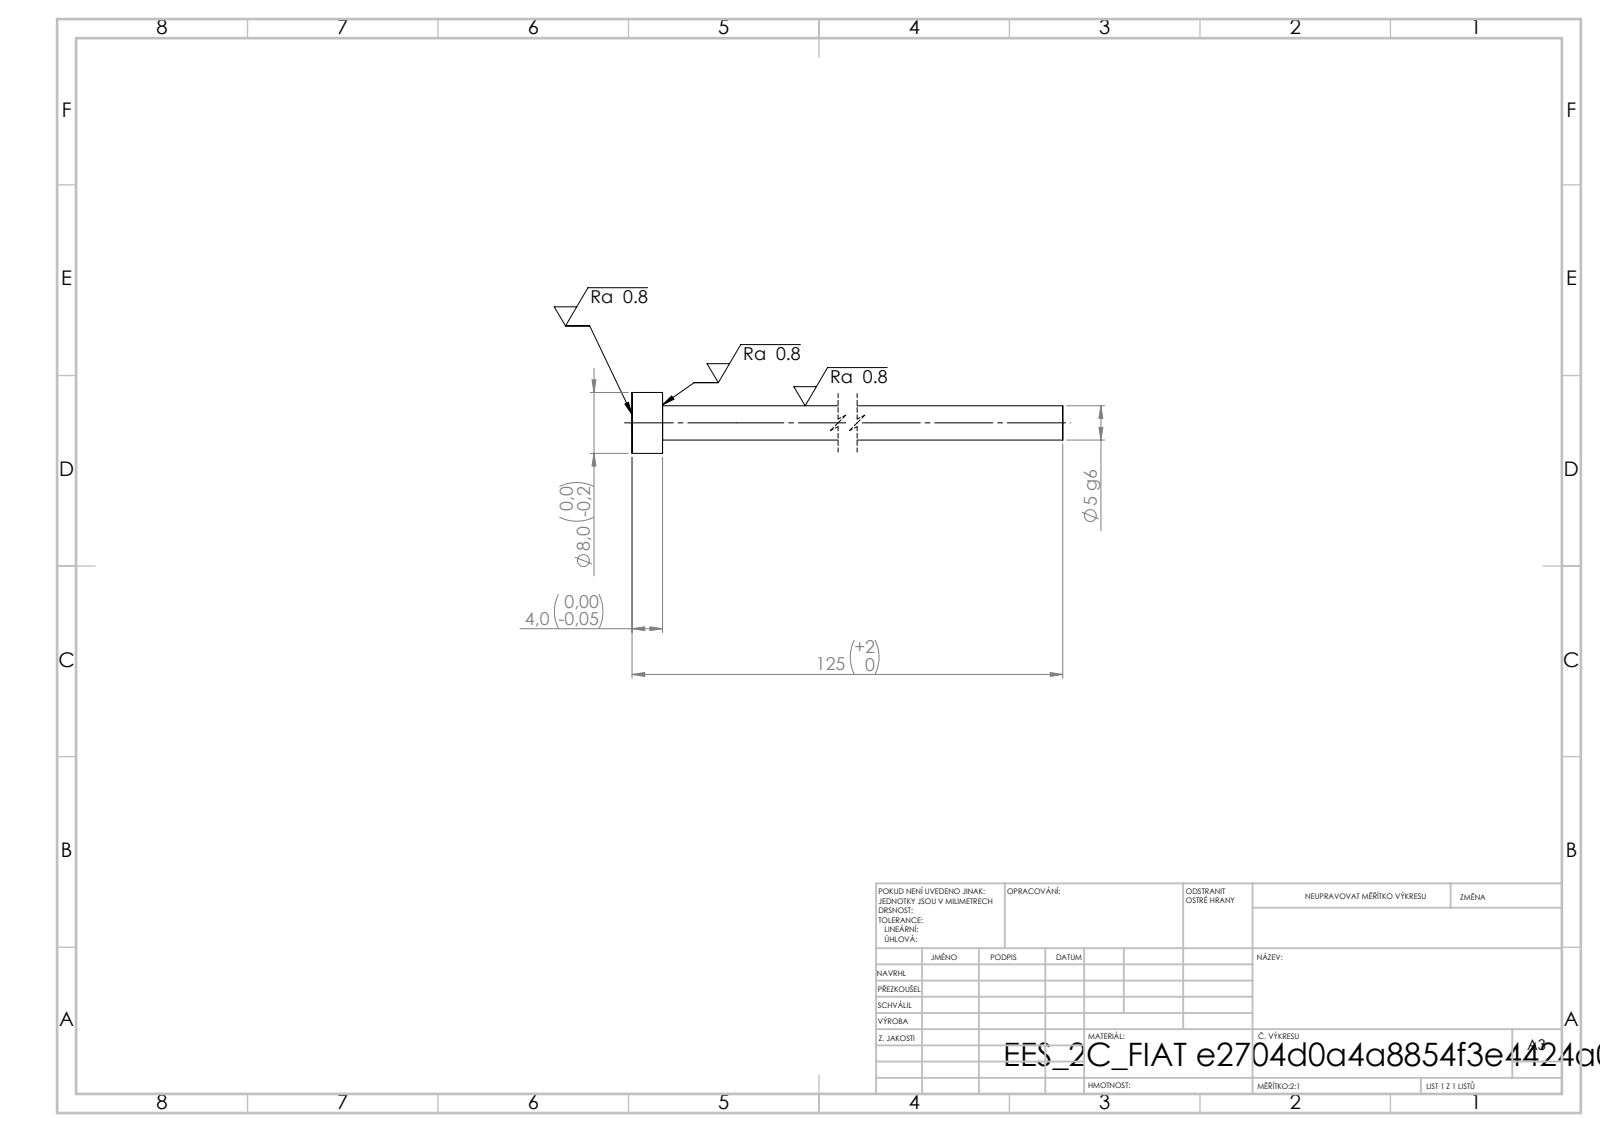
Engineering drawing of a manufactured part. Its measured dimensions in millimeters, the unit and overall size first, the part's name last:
Units: millimetres
Overall size (bounding box): 125 × 8 × 8
Round bosses / shafts (diameter × count): ⌀8 ×1, ⌀4.5 ×1
Main face-to-face distances: 4, 125, 121
Volume: 2 125 mm³ · Surface area: 1 912 mm²
Bodies: 1 solid, 7 faces (3 planar, 4 cylindrical, 0 other)
STEP written by: SolidWorks 2019 (CONFIG_CONTROL_DESIGN)
